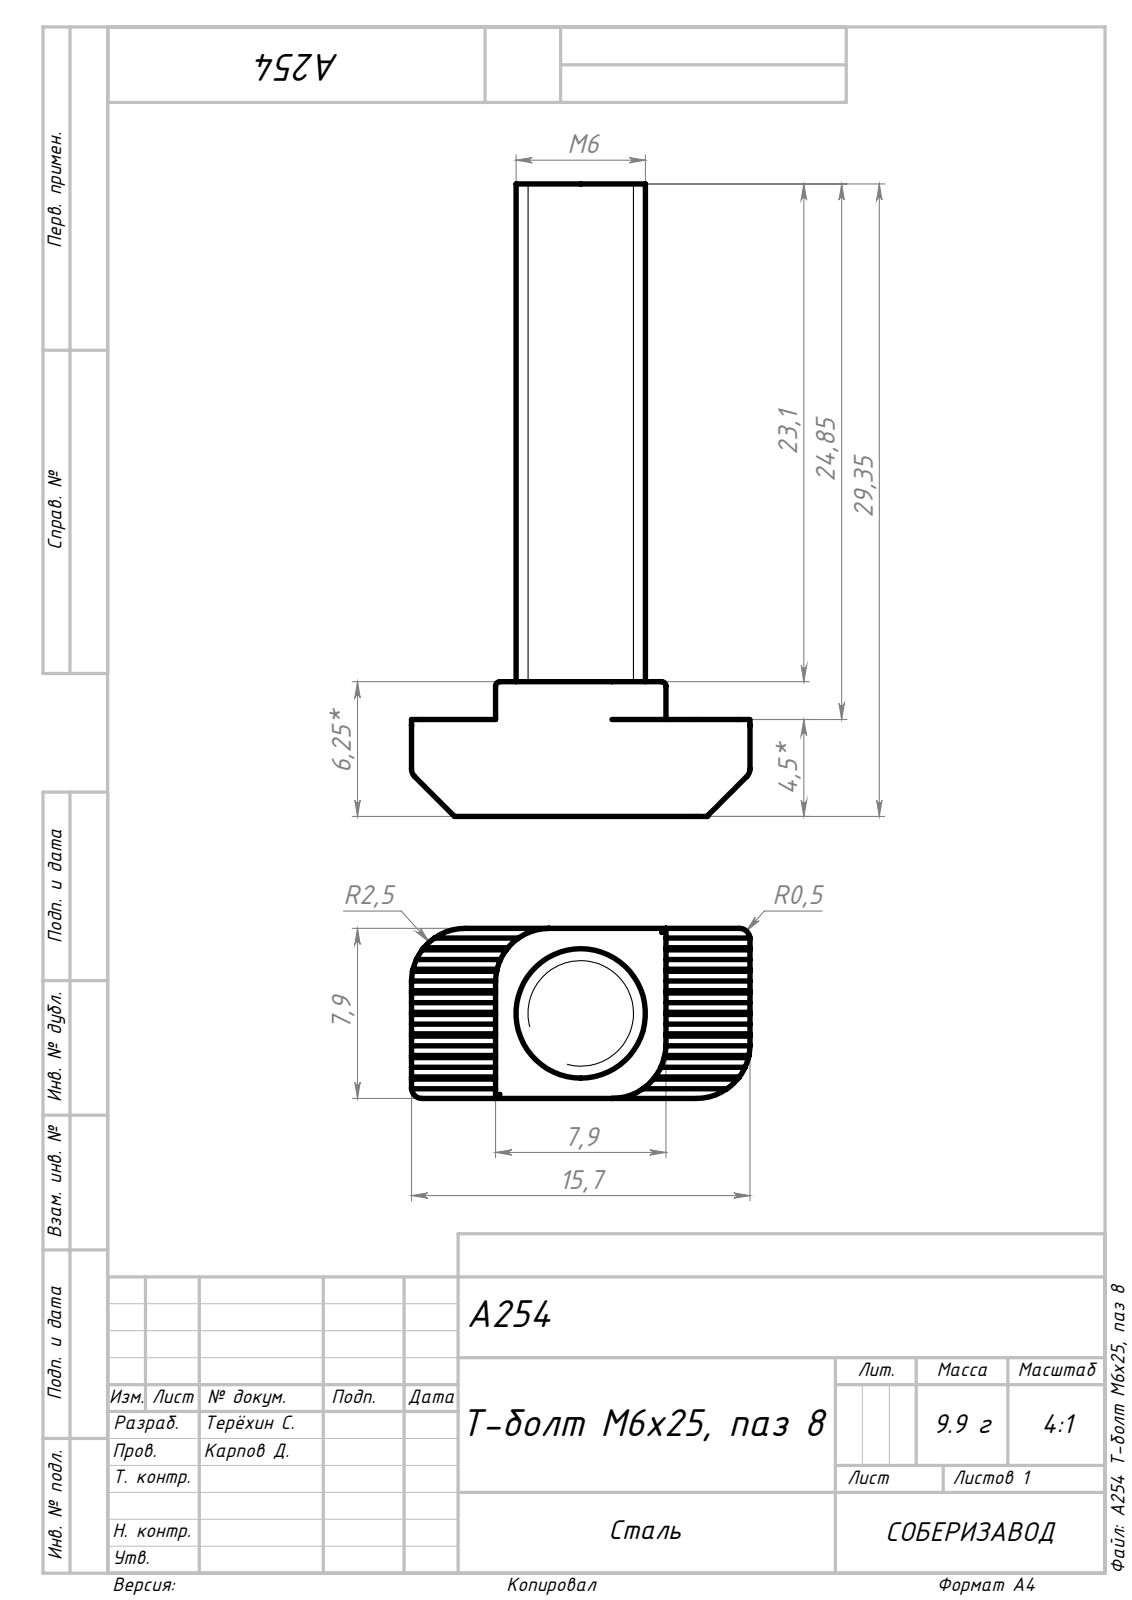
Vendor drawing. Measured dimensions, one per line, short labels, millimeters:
name: А254 Т-болт М6х25, паз 8
written by: SolidWorks 2021 (AUTOMOTIVE_DESIGN)
unit: mm
bodies: 1 solid, 83 faces (57 planar, 18 cylindrical, 8 other)
size: 29.35 × 15.7 × 7.9
volume: 1 265 mm³; area: 910 mm²
bosses: 1× ⌀6
rounds: 8× R0.5, 4× R0.2, 4× R2.5
face distances: 7.9, 1.11, 0.56, 2.22, 29.35, 6.25, 23.1, 0.55, 1.67, 3.9
